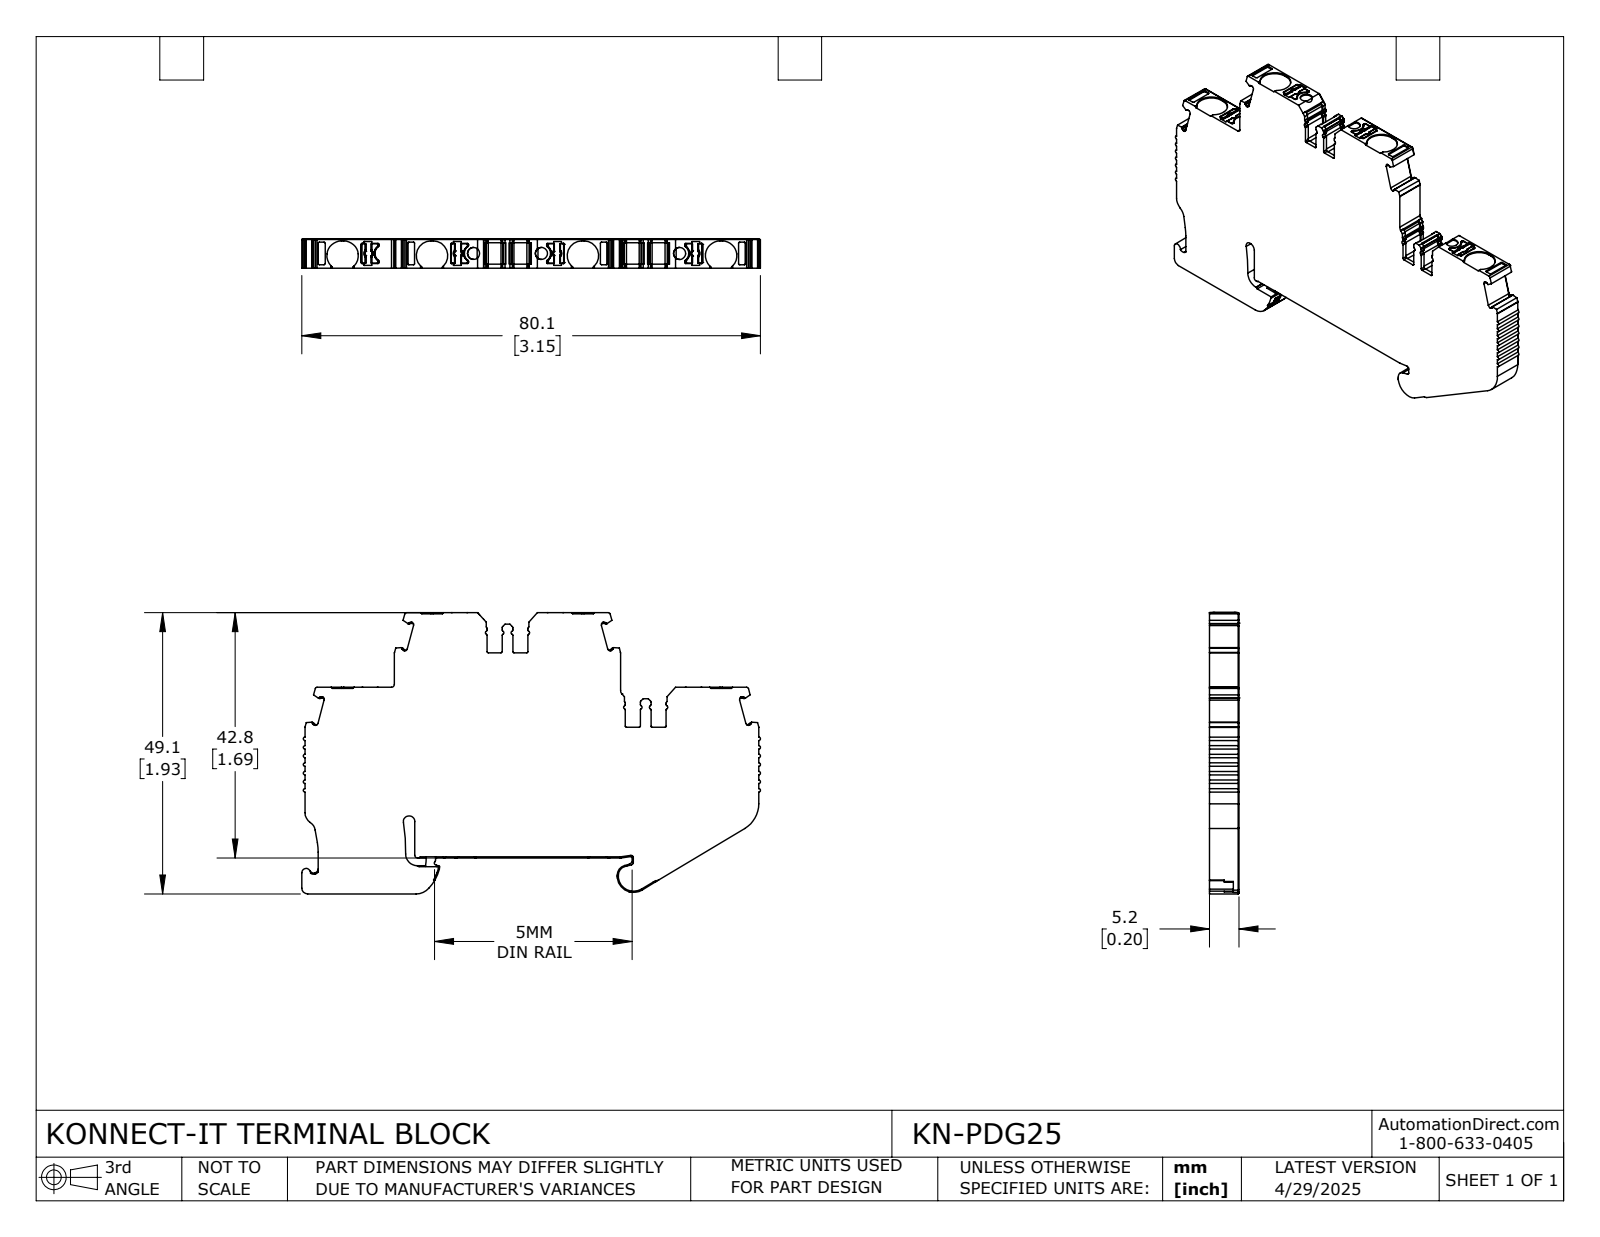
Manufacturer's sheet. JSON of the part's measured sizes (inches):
{"part_name": "KN-PDG25", "step_written_by": "SolidWorks 2024 (CONFIG_CONTROL_DESIGN)", "units": "inches", "bodies": {"solids": 1, "faces": 1035, "planar": 499, "cylindrical": 463, "other": 73}, "overall_size": [3.153, 1.933, 0.203], "volume_in3": 0.886, "surface_area_in2": 11.71, "round_holes": [[0.083, 3]], "partial_cylinders_radius": [[0.008, 99], [0.012, 59], [0.004, 41], [0.016, 25], [0.02, 20], [0.006, 16], [0.024, 9], [0.039, 9]], "face_to_face_distances": [0.203, 0.512, 1.166, 1.678, 0.246, 1.924, 0.95, 1.412, 0.504, 0.254], "hole_center_spacings": [0.466, 0.95, 1.417]}
